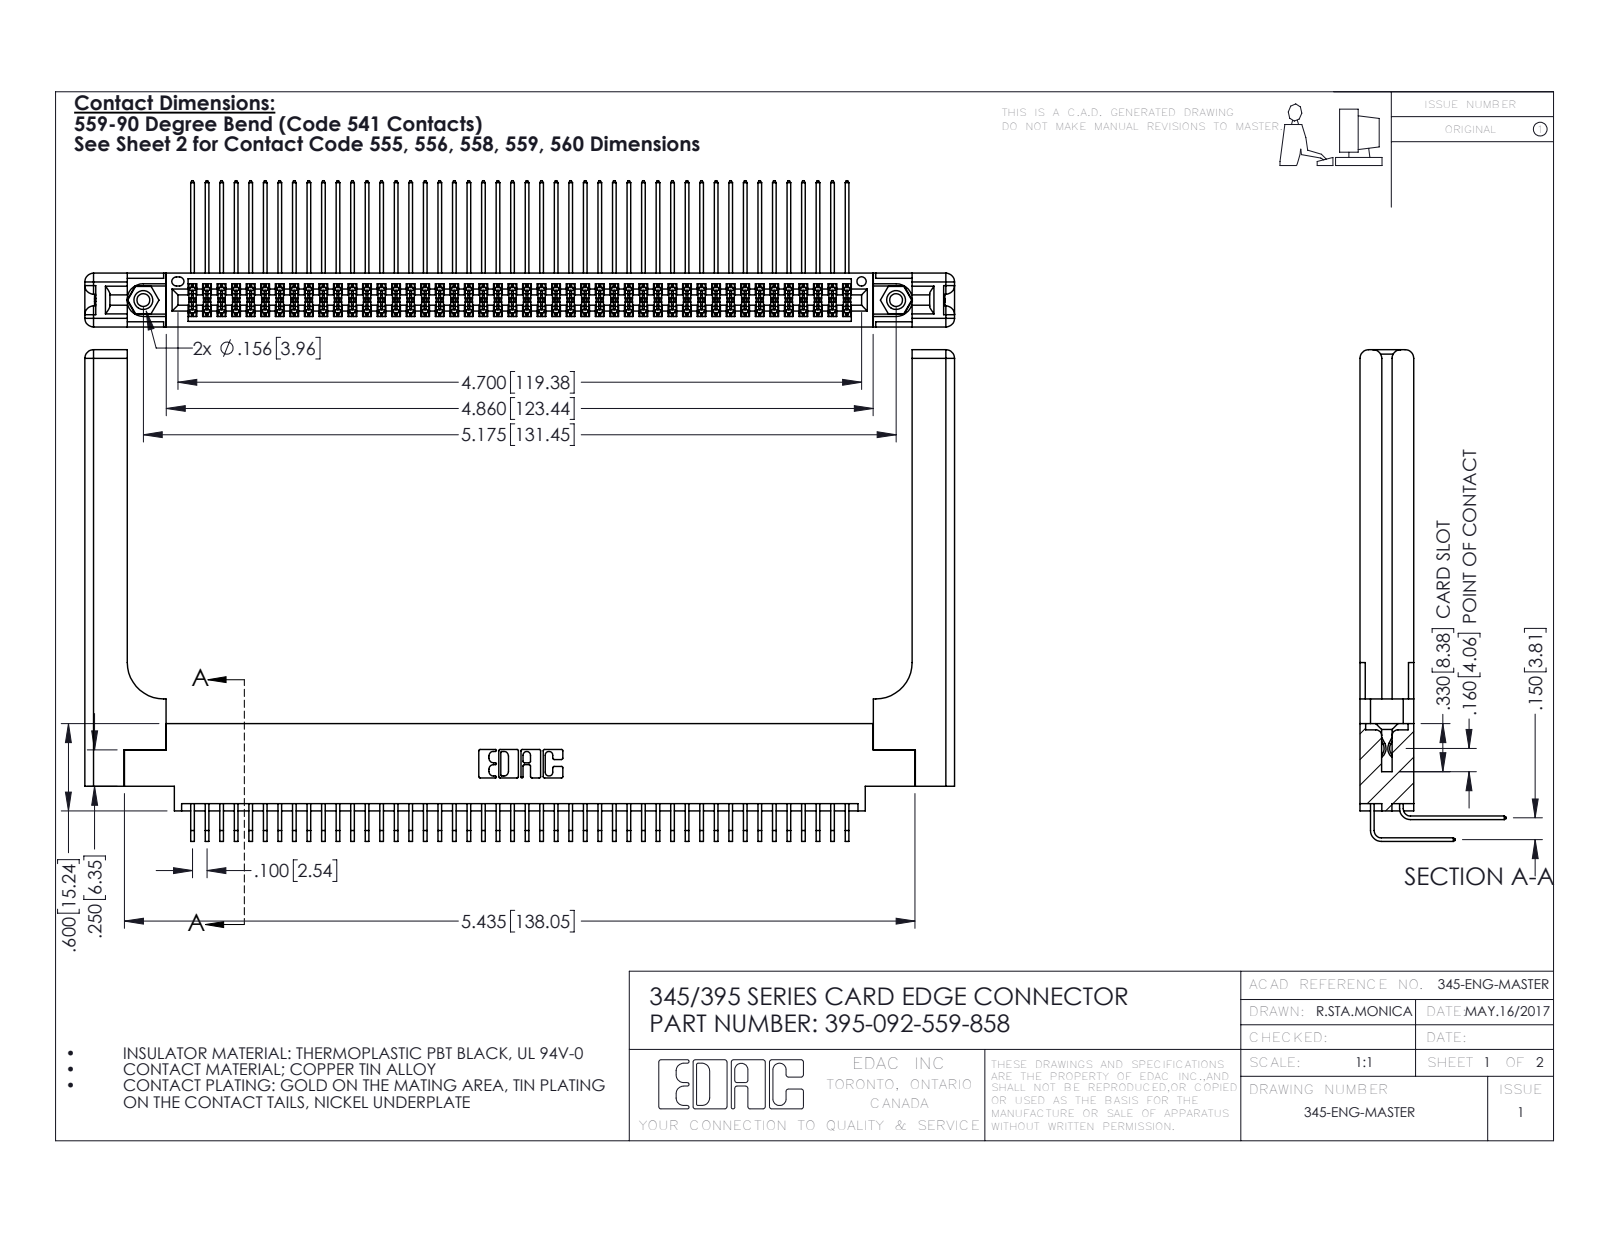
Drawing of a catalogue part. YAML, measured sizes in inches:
part_name: "395-092-559-858; 345-220-058_345-220-058; 345-250-001_345-250-001-102; 345-292-001_558 559 Tail - 1 (+2 more)"
step_written_by: "SolidWorks 2016 (CONFIG_CONTROL_DESIGN)"
units: inches
bodies: {solids: 97, faces: 5170, planar: 3452, cylindrical: 1658, other: 60}
overall_size: [5.979, 3.379, 1.005]
volume: 1.445
surface_area: 46.89
round_holes:
  - {diameter: 0.089, count: 2}
  - {diameter: 0.125, count: 2}
  - {diameter: 0.156, count: 2}
  - {diameter: 0.064, count: 1}
round_bosses_or_shafts:
  - {diameter: 0.155, count: 2}
partial_cylinders:
  - {radius: 0.006, count: 138}
  - {radius: 0.01, count: 22}
  - {radius: 0.06, count: 16}
  - {radius: 0.007, count: 6}
  - {radius: 0.031, count: 6}
  - {radius: 0.026, count: 3}
  - {radius: 0.014, count: 2}
  - {radius: 0.019, count: 2}
face_to_face_distances: [0.072, 0.37, 0.298, 0.098, 0.272, 0.025, 0.2, 0.225, 0.15, 0.175]
hole_center_spacings: [0.27, 4.939, 5.175]
